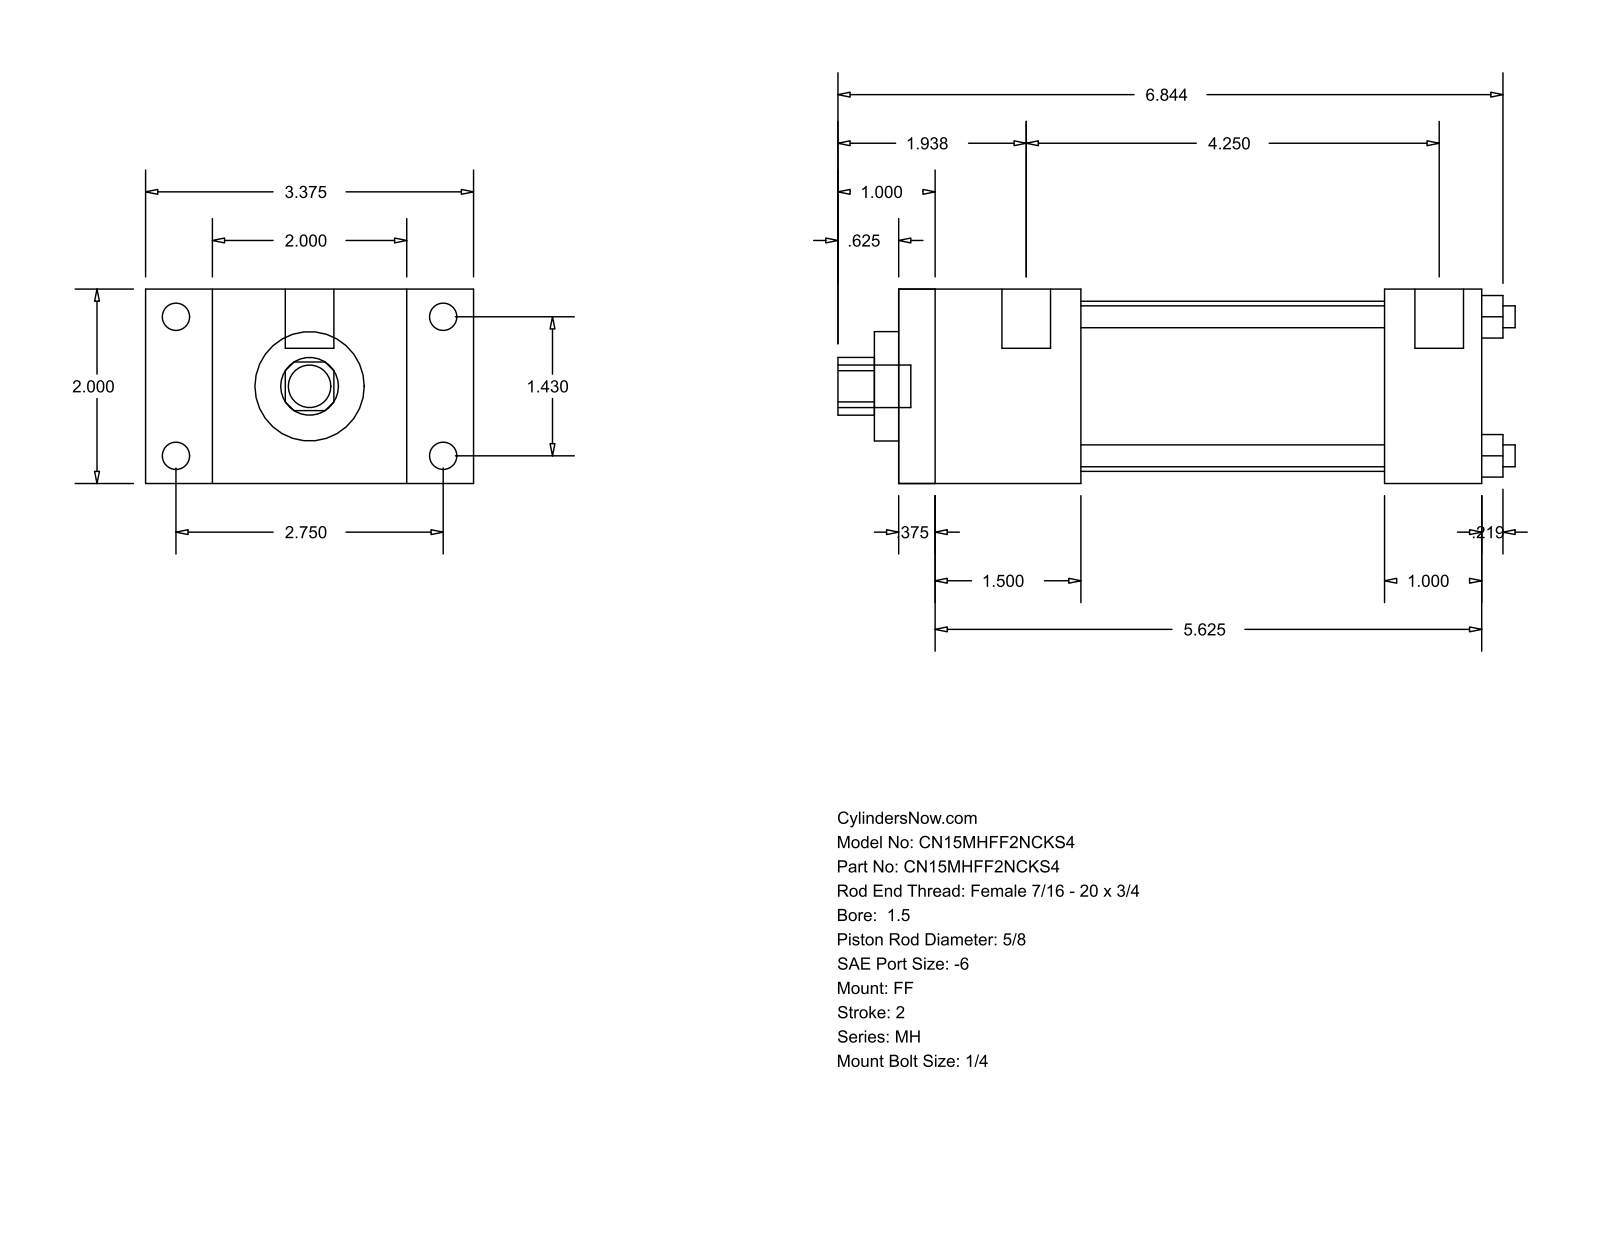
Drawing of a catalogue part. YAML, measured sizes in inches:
part_name: "MH_FF__0150_0.625"
step_written_by: "GSSL Pune (CONFIG_CONTROL_DESIGN)"
units: inches
bodies: {solids: 0, faces: 92, planar: 64, cylindrical: 28, other: 0}
overall_size: [6.969, 3.375, 2]
round_holes:
  - {diameter: 0.225, count: 4}
  - {diameter: 0.625, count: 1}
  - {diameter: 1.125, count: 1}
  - {diameter: 1.75, count: 1}
round_bosses_or_shafts:
  - {diameter: 0.281, count: 4}
  - {diameter: 0.219, count: 4}
  - {diameter: 0.5, count: 2}
  - {diameter: 0.437, count: 1}
partial_cylinders:
  - {radius: 0.297, count: 1}
face_to_face_distances: [2, 6, 0.375, 5.625, 1, 0.687, 2.687, 1.875, 1.5, 4.125]
hole_center_spacings: [1.011, 1.43, 2.022]
